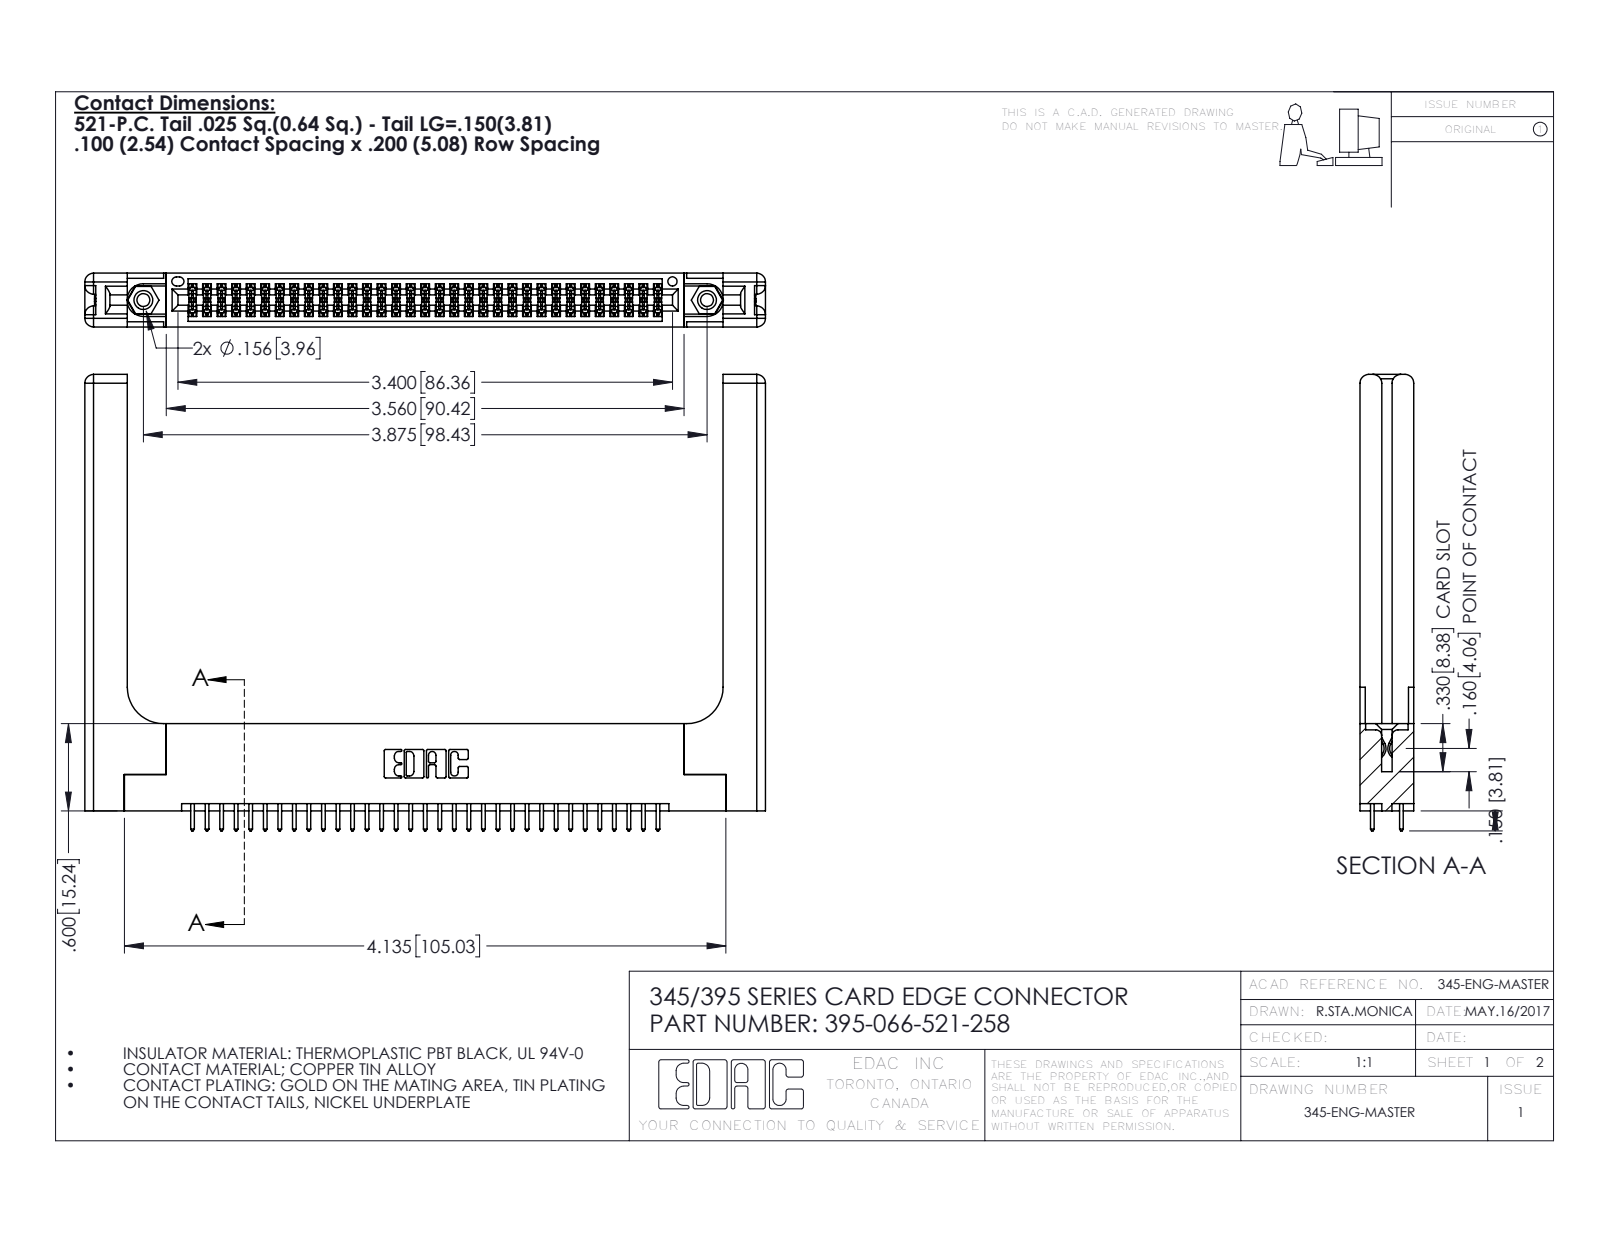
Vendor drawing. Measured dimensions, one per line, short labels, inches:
name: 345-292-001_345-293-121; 345-220-058_345-220-058; 395-066-521-258; 345-250-001_345-250-001-102 (+1 more)
written by: SolidWorks 2016 (CONFIG_CONTROL_DESIGN)
unit: in
bodies: 71 solids, 3682 faces (2406 planar, 1216 cylindrical, 60 other)
size: 4.679 × 3.137 × 0.37
volume: 1.215 in³; area: 33.5 in²
holes: 2× ⌀0.089, 2× ⌀0.125, 2× ⌀0.156, 1× ⌀0.064
bosses: 2× ⌀0.155
rounds: 99× R0.006, 66× R0.01, 22× R0.01, 16× R0.06, 6× R0.007, 6× R0.031, 3× R0.026, 2× R0.014
face distances: 0.072, 0.37, 0.298, 0.2, 0.098, 0.272, 0.025, 0.225, 0.148, 0.15
hole spacings: 0.27, 3.64, 3.875
